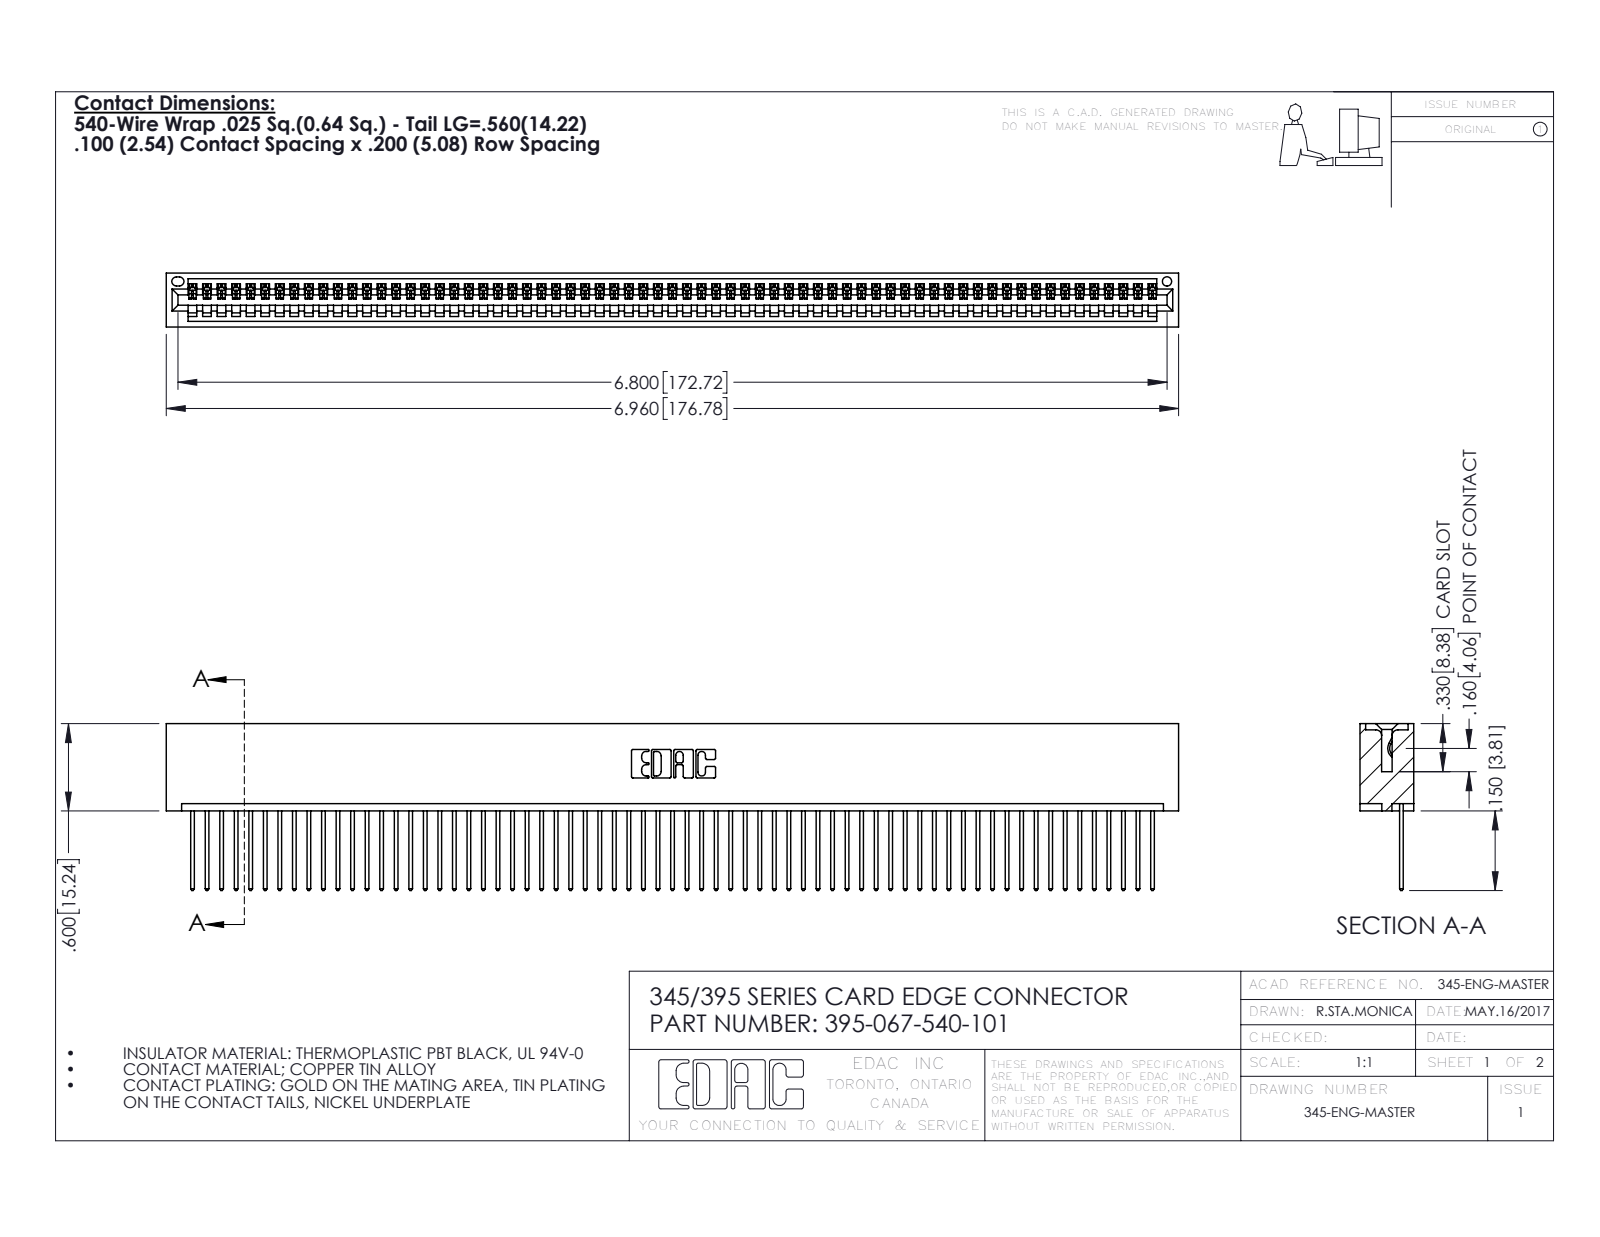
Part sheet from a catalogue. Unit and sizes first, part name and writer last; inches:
Units: inches
Overall size (bounding box): 6.96 × 1.147 × 0.37
Round holes (diameter × count): ⌀0.064 ×1
Partial cylindrical surfaces — rounded edges, fillets, slot ends (radius × count): R0.006 ×134, R0.01 ×134, R0.01 ×22, R0.007 ×6, R0.031 ×6, R0.026 ×3, R0.031 ×2, R0.04 ×2
Main face-to-face distances: 0.072, 0.298, 0.098, 0.272, 0.025, 0.37, 0.2, 0.225, 0.149, 0.072
Volume: 1.078 in³ · Surface area: 38.23 in²
Bodies: 68 solids, 4004 faces (2756 planar, 1248 cylindrical, 0 other)
Part name (STEP PRODUCT): 395-067-540-101; 345-292-001_345-293-140; 345 Part_No Mounting Lugs
STEP written by: SolidWorks 2016 (CONFIG_CONTROL_DESIGN)
